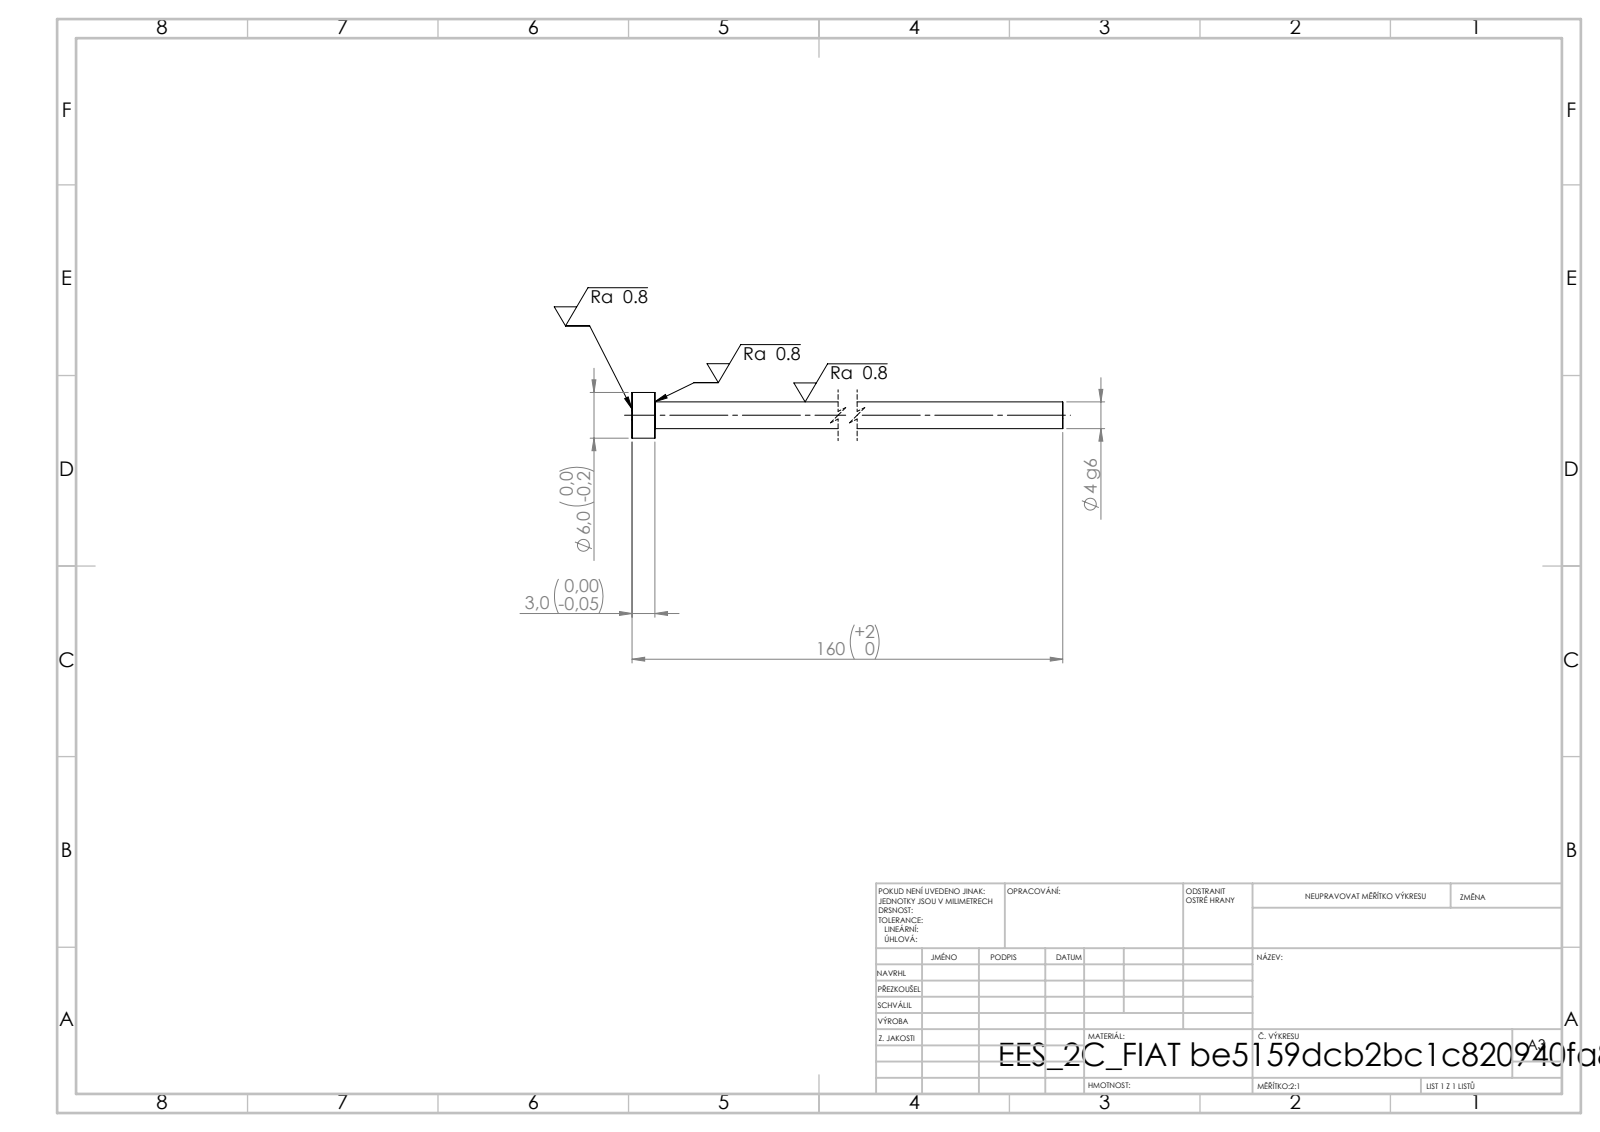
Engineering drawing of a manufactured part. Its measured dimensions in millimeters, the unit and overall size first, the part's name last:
Units: millimetres
Overall size (bounding box): 160 × 6 × 6
Round bosses / shafts (diameter × count): ⌀6 ×1, ⌀3.5 ×1
Main face-to-face distances: 3, 160, 157
Volume: 1 595 mm³ · Surface area: 1 839 mm²
Bodies: 1 solid, 7 faces (3 planar, 4 cylindrical, 0 other)
STEP written by: SolidWorks 2019 (CONFIG_CONTROL_DESIGN)
